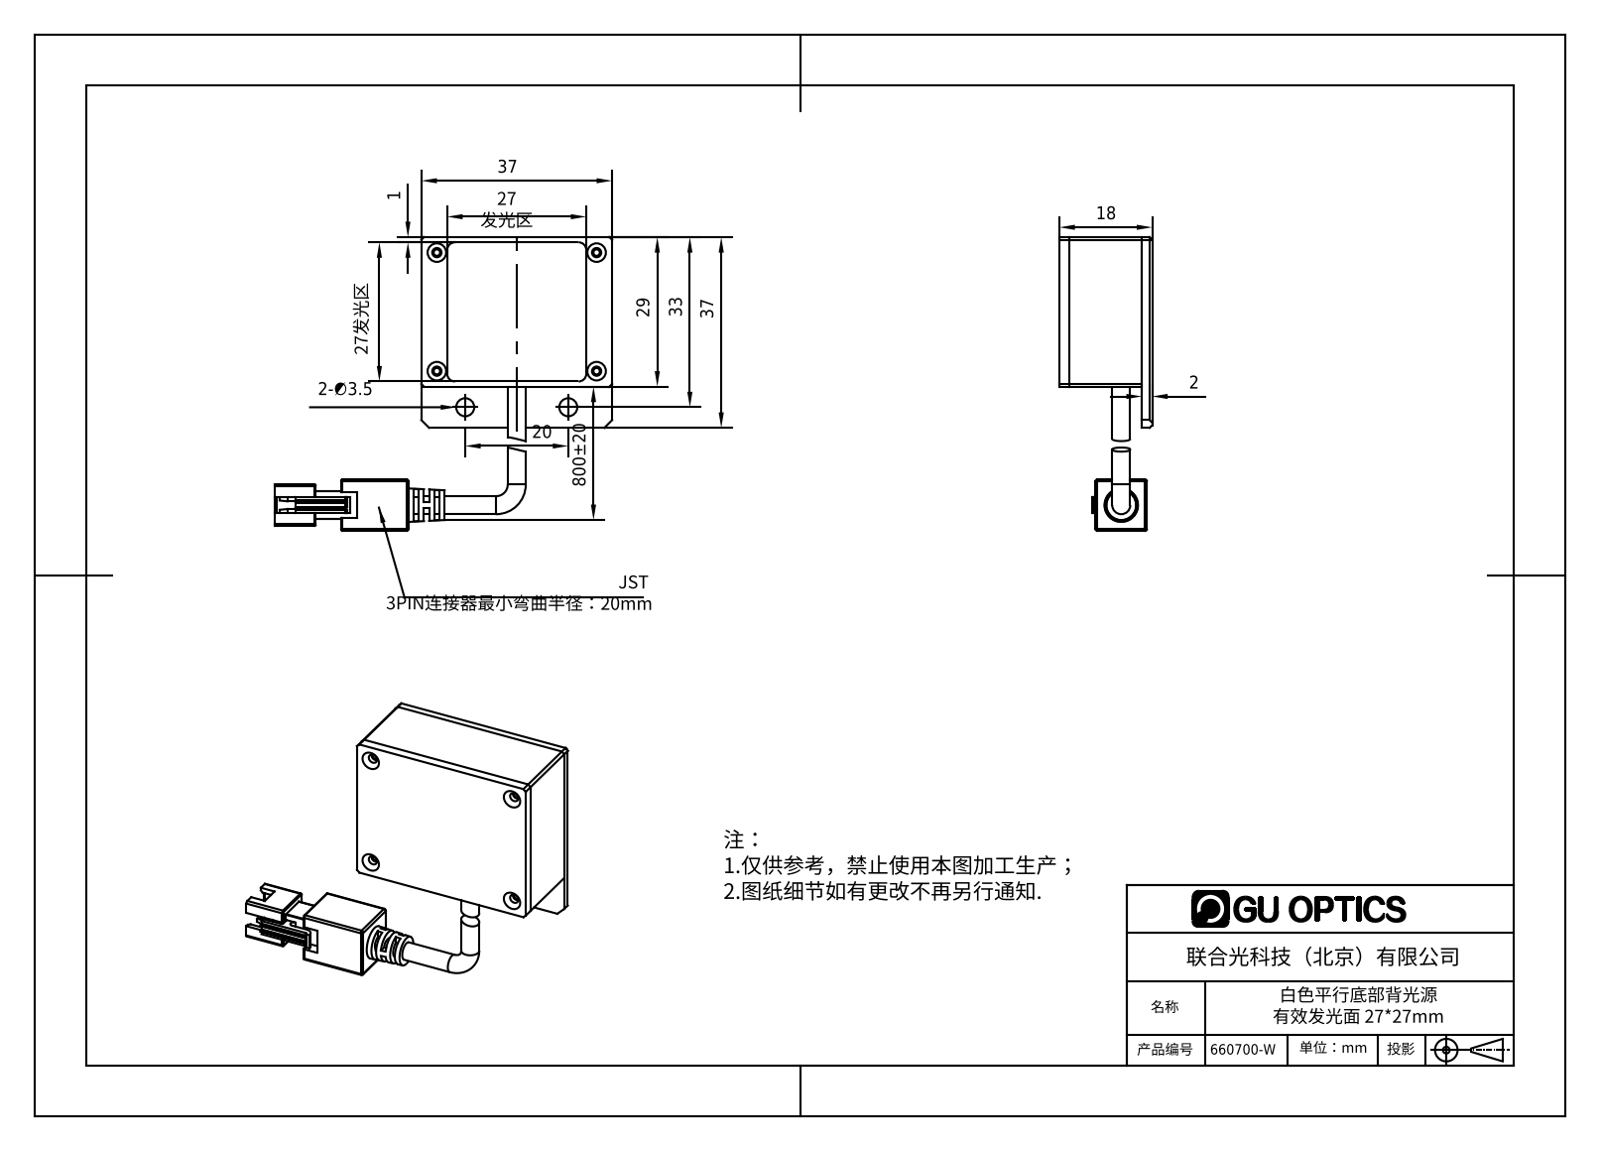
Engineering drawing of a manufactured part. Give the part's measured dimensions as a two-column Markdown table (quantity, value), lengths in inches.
| quantity | value |
| --- | --- |
| part name | 660700-W |
| STEP written by | SolidWorks 2016 (AUTOMOTIVE_DESIGN) |
| units | inches |
| bodies | 6 solids, 470 faces (229 planar, 122 cylindrical, 119 other) |
| overall size | 2.579 × 2.244 × 0.713 |
| volume | 0.709 in³ |
| surface area | 20.31 in² |
| round holes (diameter × count) | 0.049 × 4, 0.063 × 4, 0.071 × 4, 0.079 × 4, 0.094 × 4, 0.138 × 2 |
| round bosses / shafts (diameter × count) | 0.138 × 2 |
| partial cylindrical surfaces (radius × count) | 0.004 × 15, 0.008 × 13, 0.016 × 12, 0.039 × 4, 0.059 × 4, 0.012 × 1, 0.027 × 1, 0.055 × 1 |
| main face-to-face distances | 0.63, 0.079, 0.551, 0.709, 0.039, 1.102, 0.197, 0.083, 0.713, 0.634 |
| hole center spacings | 0.35, 0.906, 1.041, 1.201, 1.22, 1.52, 1.55, 0.787 |
